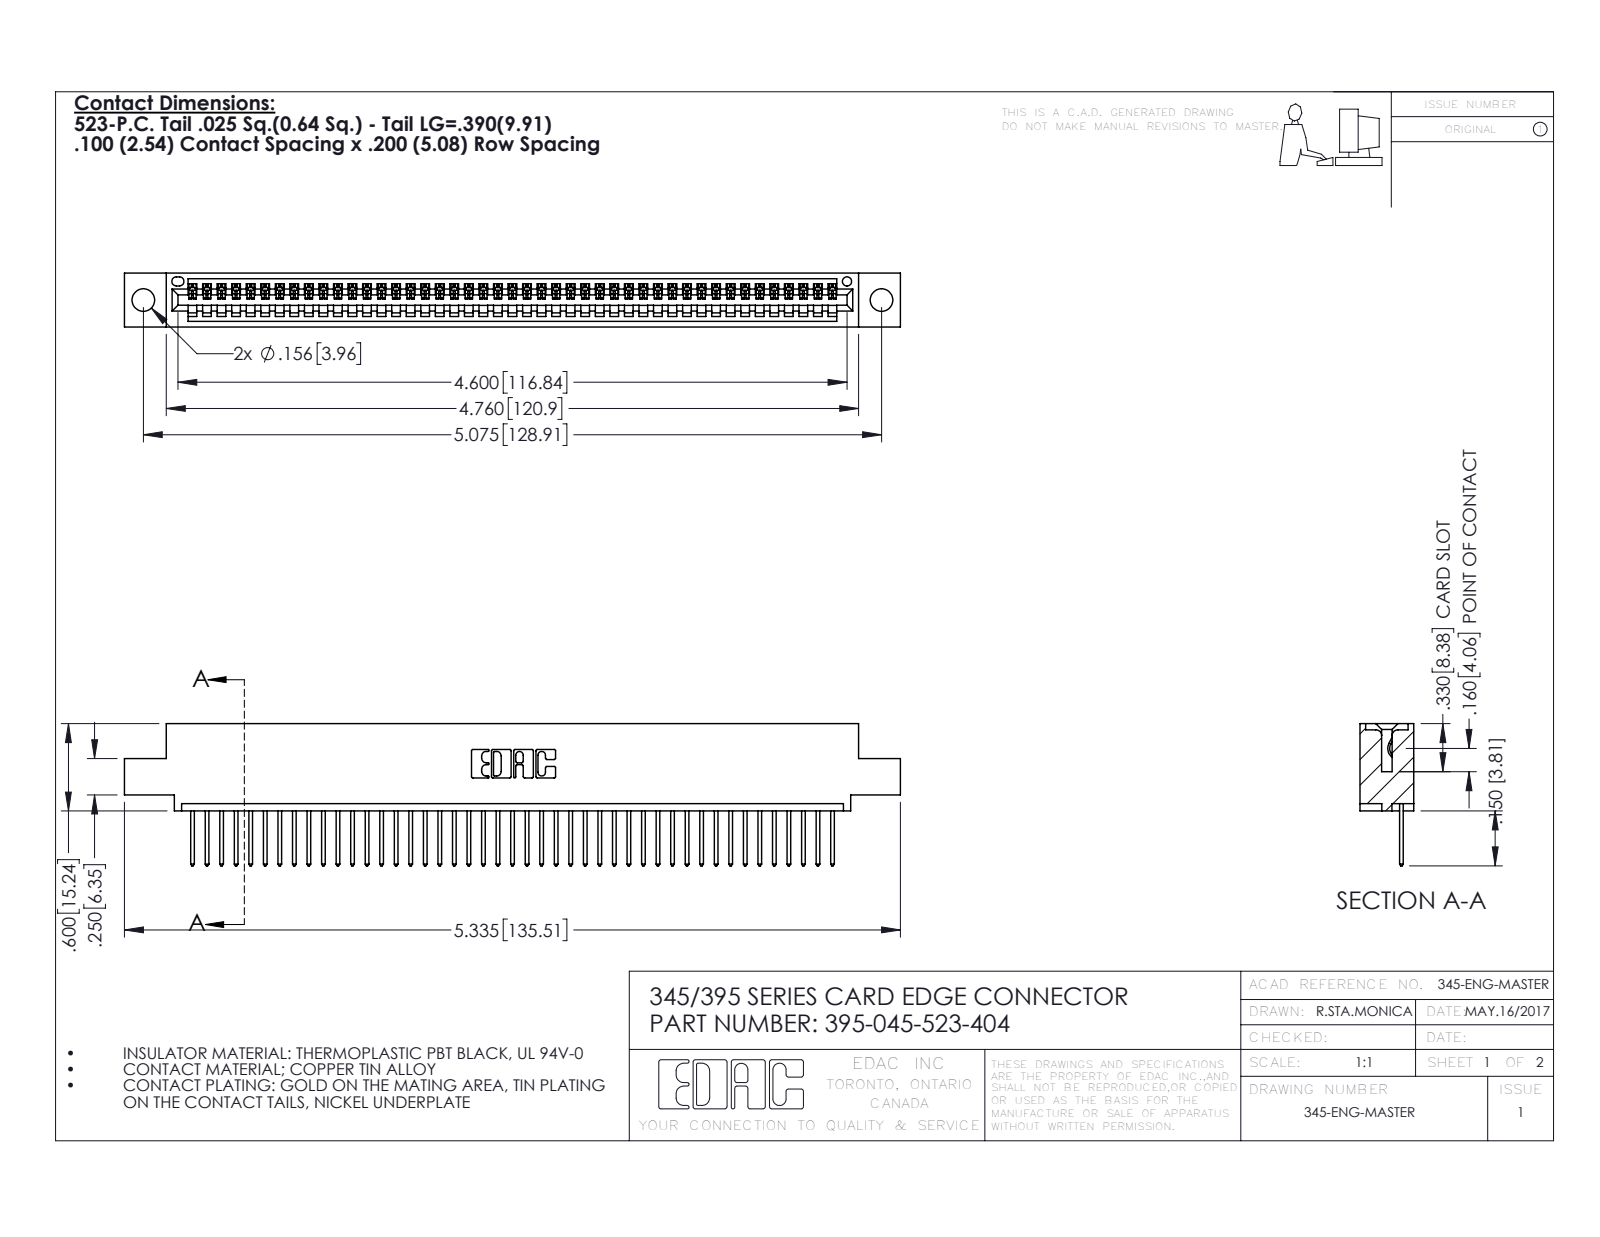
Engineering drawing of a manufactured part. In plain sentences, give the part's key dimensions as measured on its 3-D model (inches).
The part is named "345-292-001_345-293-123; 395-045-523-404; 345 Part_0.110 Offset - 0.156 Dia-TH". Its 3-D file was written by "SolidWorks 2016 (CONFIG_CONTROL_DESIGN)". It is 46 solids with 2740 faces: 1884 planar, 856 cylindrical and 0 other. Overall it measures 5.335 by 0.977 by 0.37 inches. Its volume is 0.776 cubic inches and its surface area 26.16 square inches. Round holes: 2 of diameter 0.156, 1 of diameter 0.064. Partial cylindrical surfaces (rounded edges, fillets, slot ends): 90 of radius 0.006, 90 of radius 0.01, 22 of radius 0.01, 6 of radius 0.007, 6 of radius 0.031, 3 of radius 0.026, 2 of radius 0.031, 2 of radius 0.04. The main face-to-face distances are 0.298, 0.072, 0.37, 0.2, 0.098, 0.272, 0.025, 0.225, 0.149, 0.072. The hole center spacings are 0.27, 4.839, 5.075.
